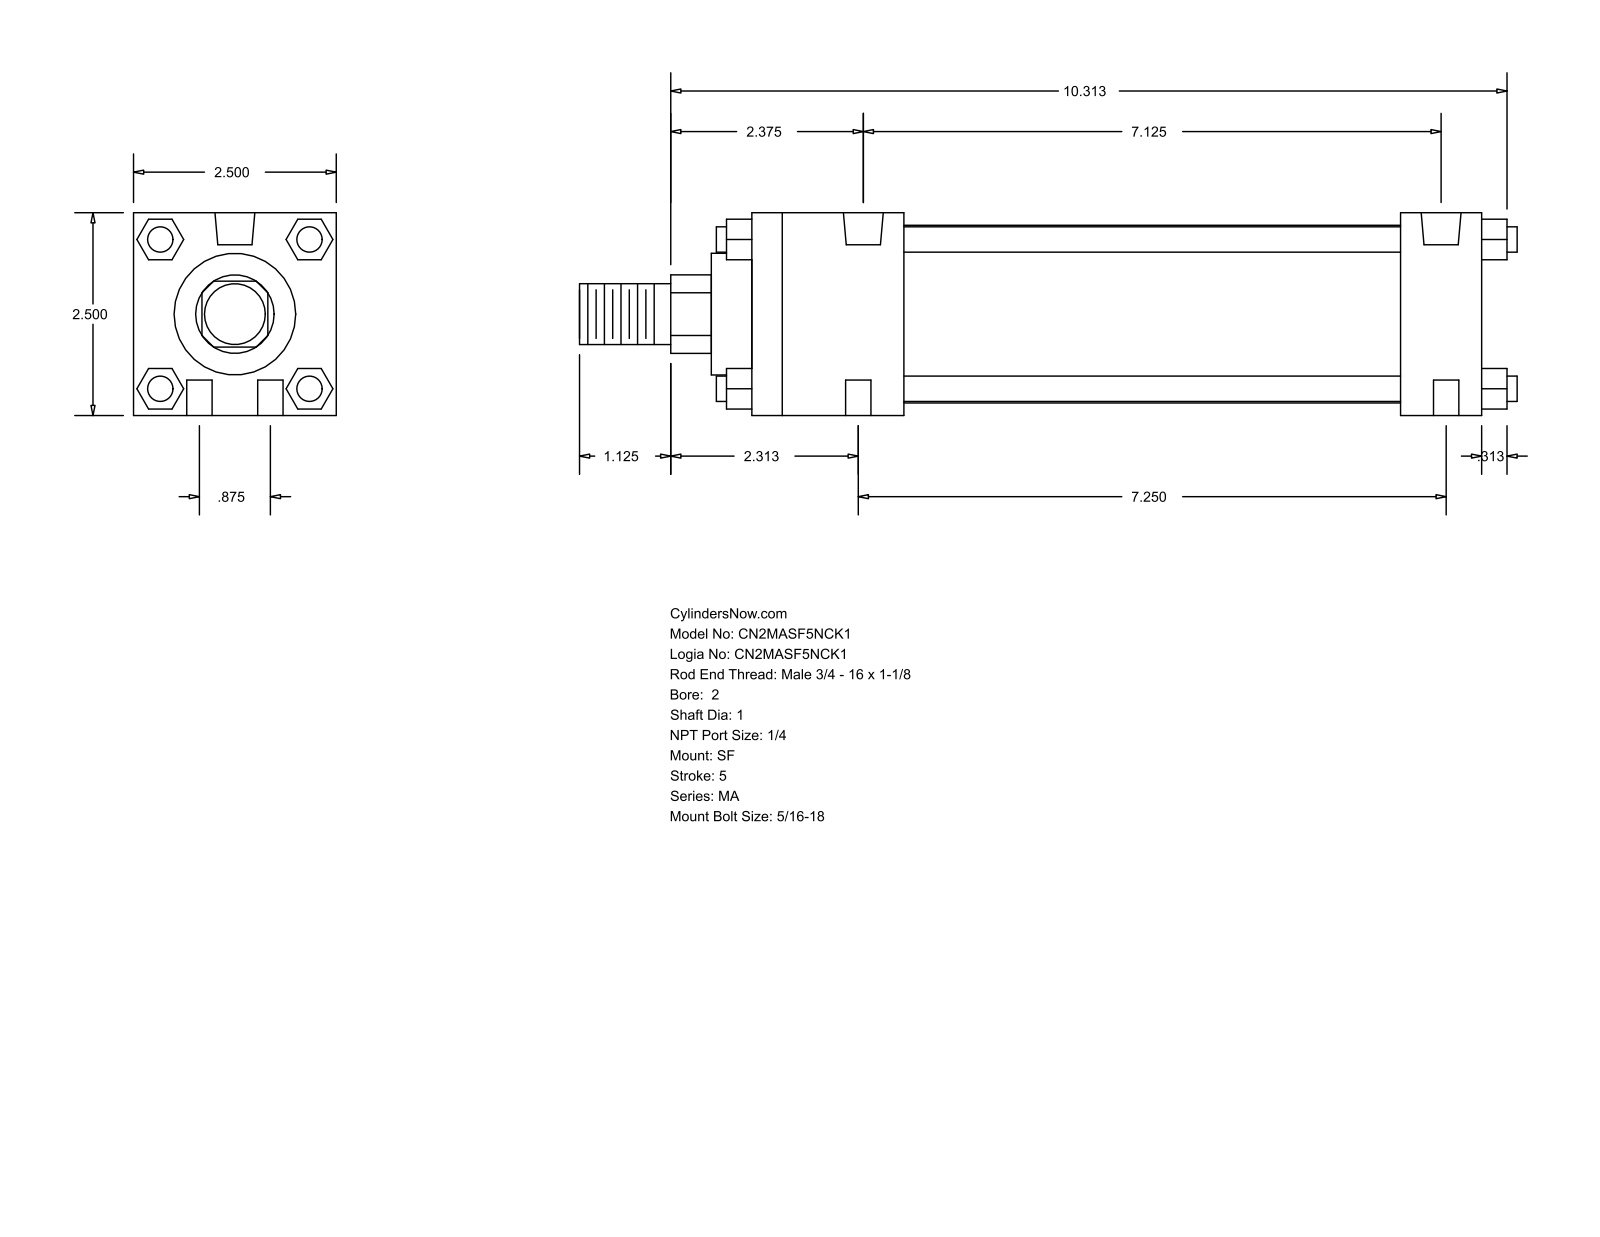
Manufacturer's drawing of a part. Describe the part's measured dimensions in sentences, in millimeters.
The part is named "MA_SF__0200_1". Its 3-D file was written by "GSSL Pune (CONFIG_CONTROL_DESIGN)". It is 0 solids with 124 faces: 94 planar, 30 cylindrical and 0 other. Overall it measures 293.69 by 63.5 by 63.5 millimeters. Round holes: 6 of diameter 7.94, 2 of diameter 12.49. Round bosses or shafts: 4 of diameter 7.94, 1 of diameter 55.63, 1 of diameter 38.1, 1 of diameter 25.4, 1 of diameter 19.05. Partial cylindrical surfaces (rounded edges, fillets, slot ends): 1 of radius 12.29. The main face-to-face distances are 63.5, 228.6, 12.7, 25.4, 203.2, 47.63, 155.57, 180.97, 23.37, 40.47. The hole center spacings are 11.22, 182.9, 22.22, 180.97, 184.15, 185.49.
